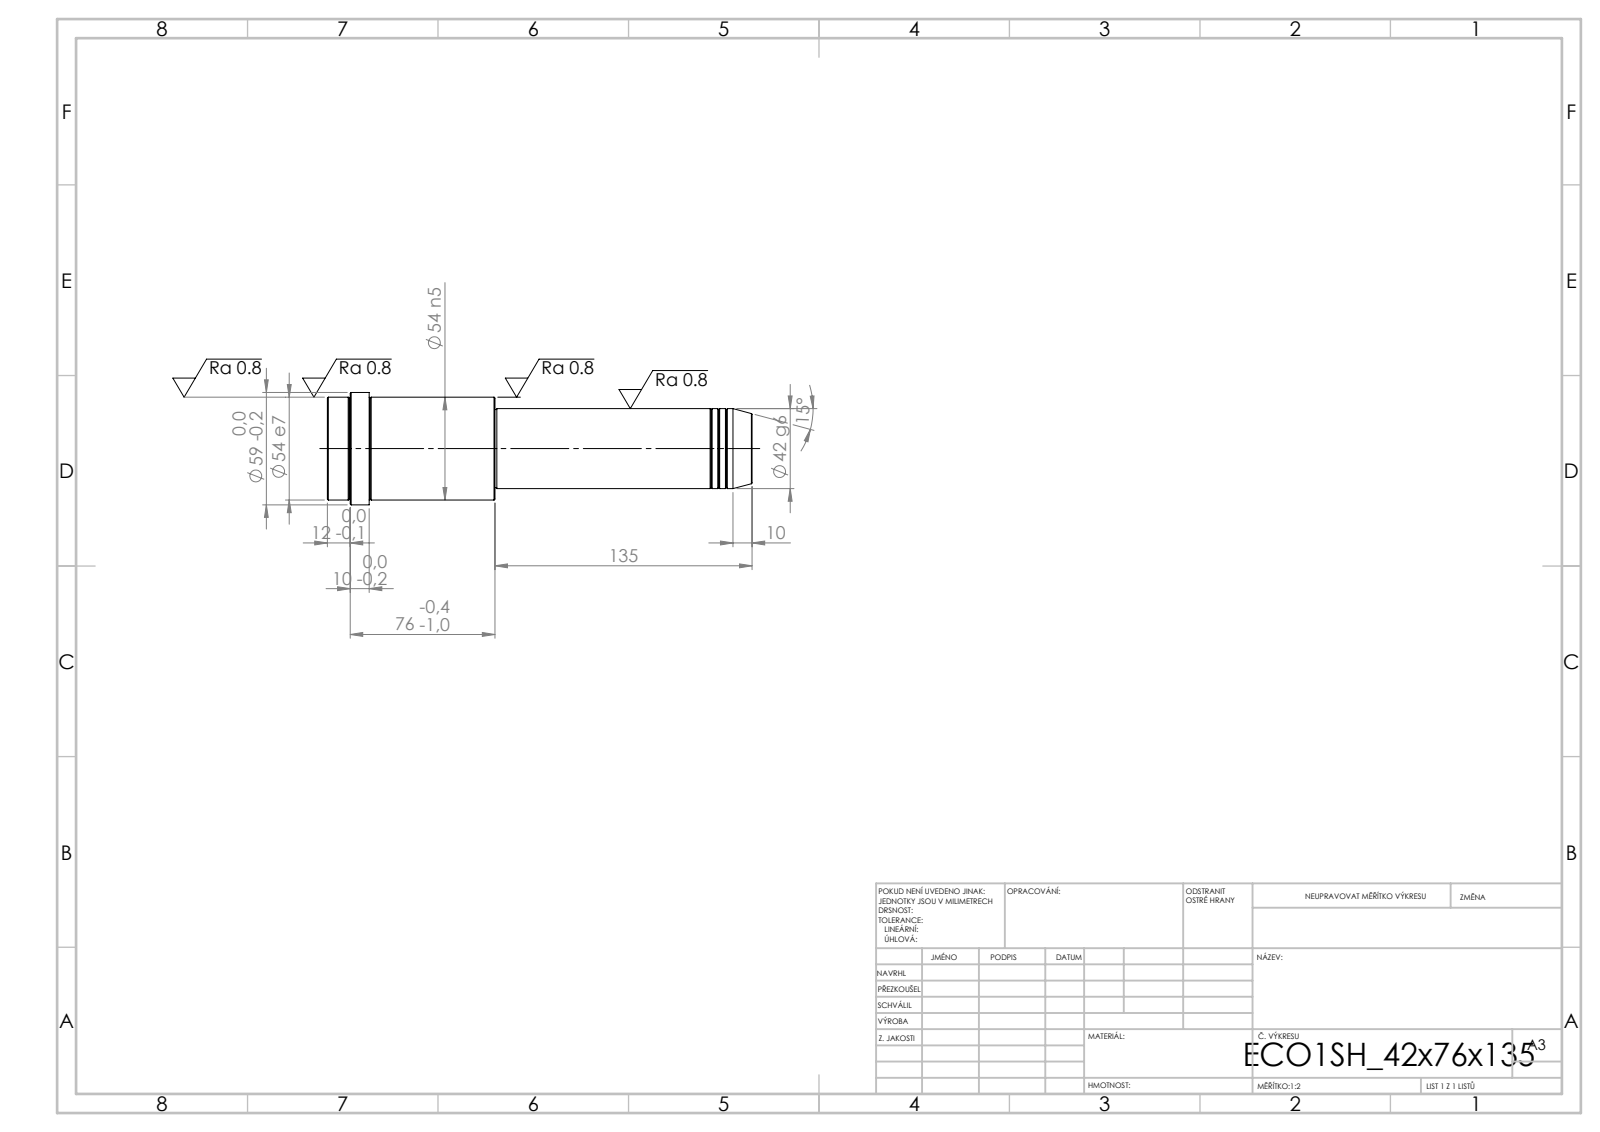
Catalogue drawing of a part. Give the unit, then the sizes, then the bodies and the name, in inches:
Units: inches
Overall size (bounding box): 8.78 × 2.323 × 2.323
Round bosses / shafts (diameter × count): ⌀2.323 ×1, ⌀2.126 ×1, ⌀1.654 ×1, ⌀1.614 ×1
Main face-to-face distances: 8.78, 5.315, 3.465, 7.913, 2.598, 0.866, 8.307, 2.992, 0.394, 0.472
Volume: 23.85 in³ · Surface area: 59.46 in²
Bodies: 1 solid, 52 faces (6 planar, 16 cylindrical, 30 other)
STEP written by: SolidWorks 2019 (CONFIG_CONTROL_DESIGN)
